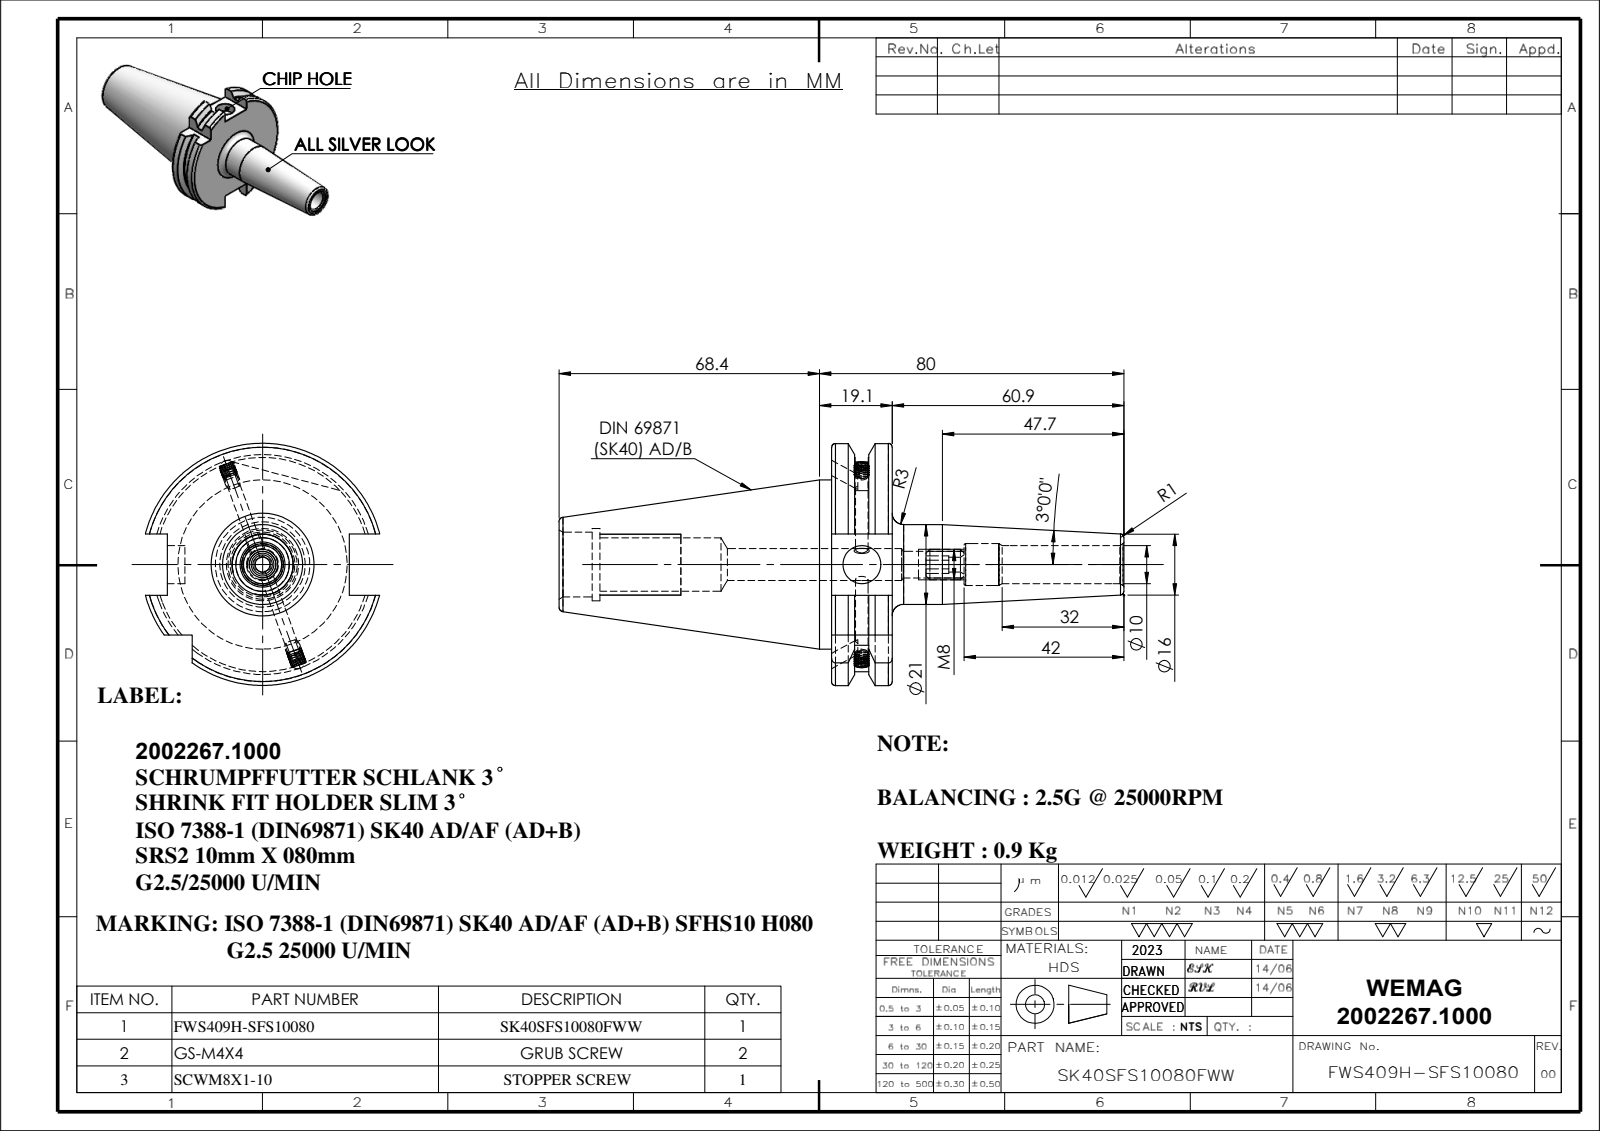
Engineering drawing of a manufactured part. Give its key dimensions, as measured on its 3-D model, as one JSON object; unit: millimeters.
{"part_name": "SK40SFS10080FWW; GS-M4X4_DIN 913 - M4 x 4-N; SCWM8X1-10; 91406-SRS210080", "step_written_by": "SolidWorks 2018 (CONFIG_CONTROL_DESIGN)", "units": "millimeters", "bodies": {"solids": 4, "faces": 224, "planar": 56, "cylindrical": 60, "other": 108}, "overall_size": [148.4, 63.55, 61.48], "volume_mm3": 116382, "surface_area_mm2": 26521, "round_holes": [[10, 2], [3.3, 1], [3.9, 1], [7, 1], [8.4, 1], [11, 1], [14, 1], [17, 1], [19, 1]], "round_bosses_or_shafts": [[4, 2], [44.45, 1], [21, 1], [8, 1]], "partial_cylinders_radius": [[28.12, 1], [31.77, 1]], "face_to_face_distances": [15.9, 16.1, 47.8, 60.9, 76.8, 71.6, 87.5, 10.7, 77.63, 66.93]}
